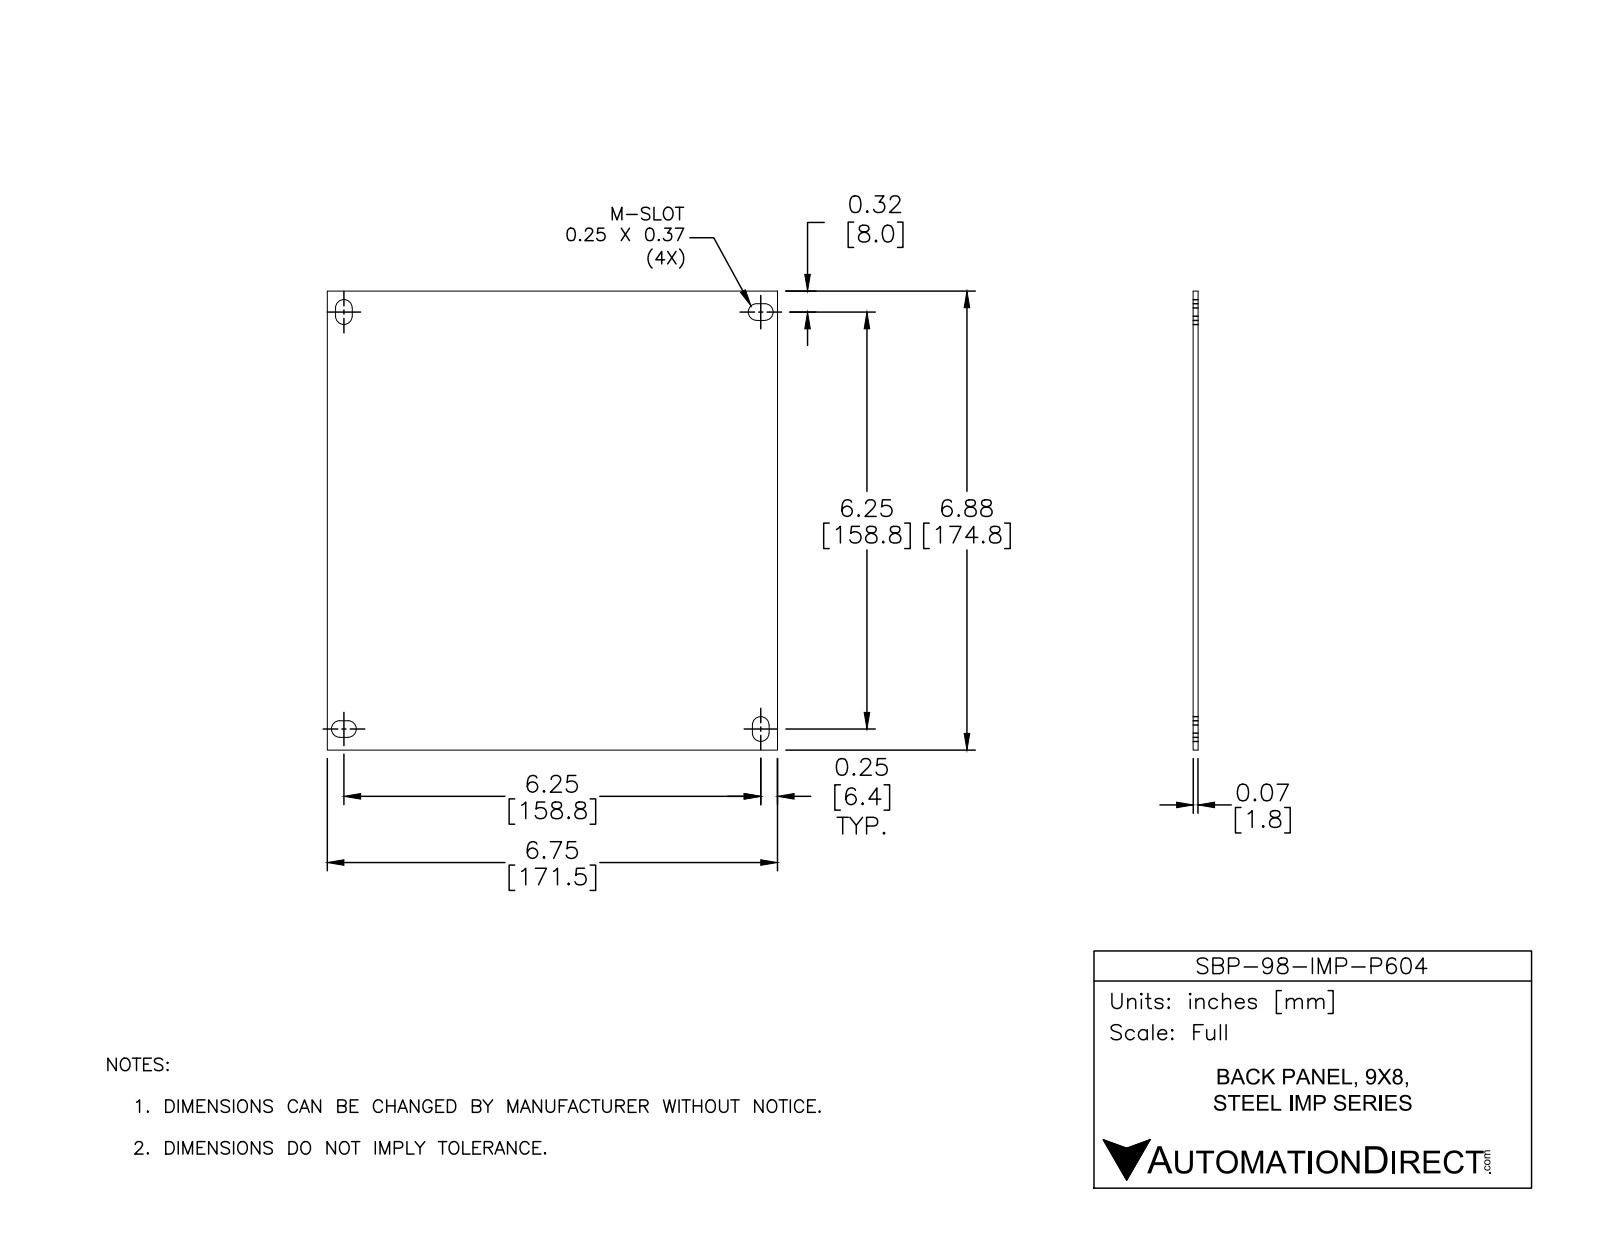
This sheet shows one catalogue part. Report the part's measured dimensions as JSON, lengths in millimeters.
{"part_name": "SBP-98-IMP-P604", "step_written_by": "SolidWorks 2016 (AUTOMOTIVE_DESIGN)", "units": "millimeters", "bodies": {"solids": 1, "faces": 24, "planar": 14, "cylindrical": 10, "other": 0}, "overall_size": [174.8, 171.5, 1.6], "volume_mm3": 48440, "surface_area_mm2": 60810, "partial_cylinders_radius": [[3.2, 8]], "face_to_face_distances": [1.6, 171.5, 174.8, 6.4, 158.8, 3.2, 168.3, 152.4, 161.9, 6.4]}
